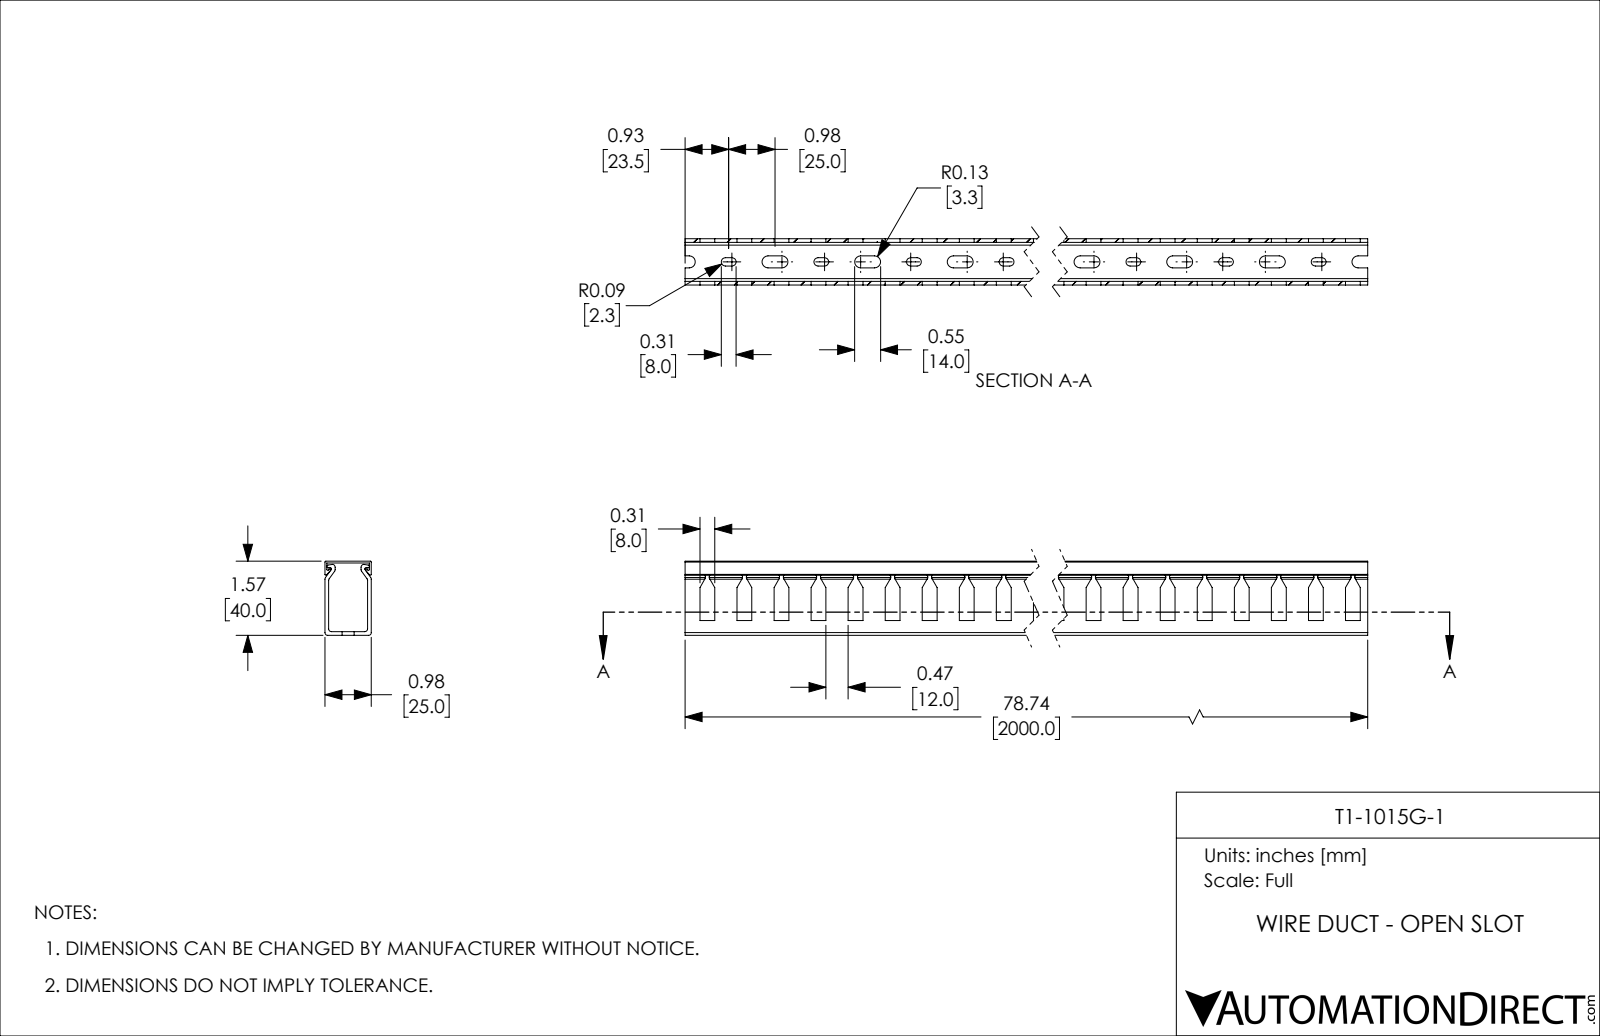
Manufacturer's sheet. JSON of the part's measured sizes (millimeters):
{"part_name": "T1-1015W-1", "step_written_by": "SolidWorks 2021 (CONFIG_CONTROL_DESIGN)", "units": "millimeters", "bodies": {"solids": 2, "faces": 945, "planar": 514, "cylindrical": 431, "other": 0}, "overall_size": [2000, 40, 25], "volume_mm3": 482780, "surface_area_mm2": 572942, "partial_cylinders_radius": [[2.25, 80], [3.25, 80], [1.5, 12], [0.5, 8], [0.75, 6]], "face_to_face_distances": [2, 23, 1, 25, 21, 40, 39, 37, 38, 24]}
